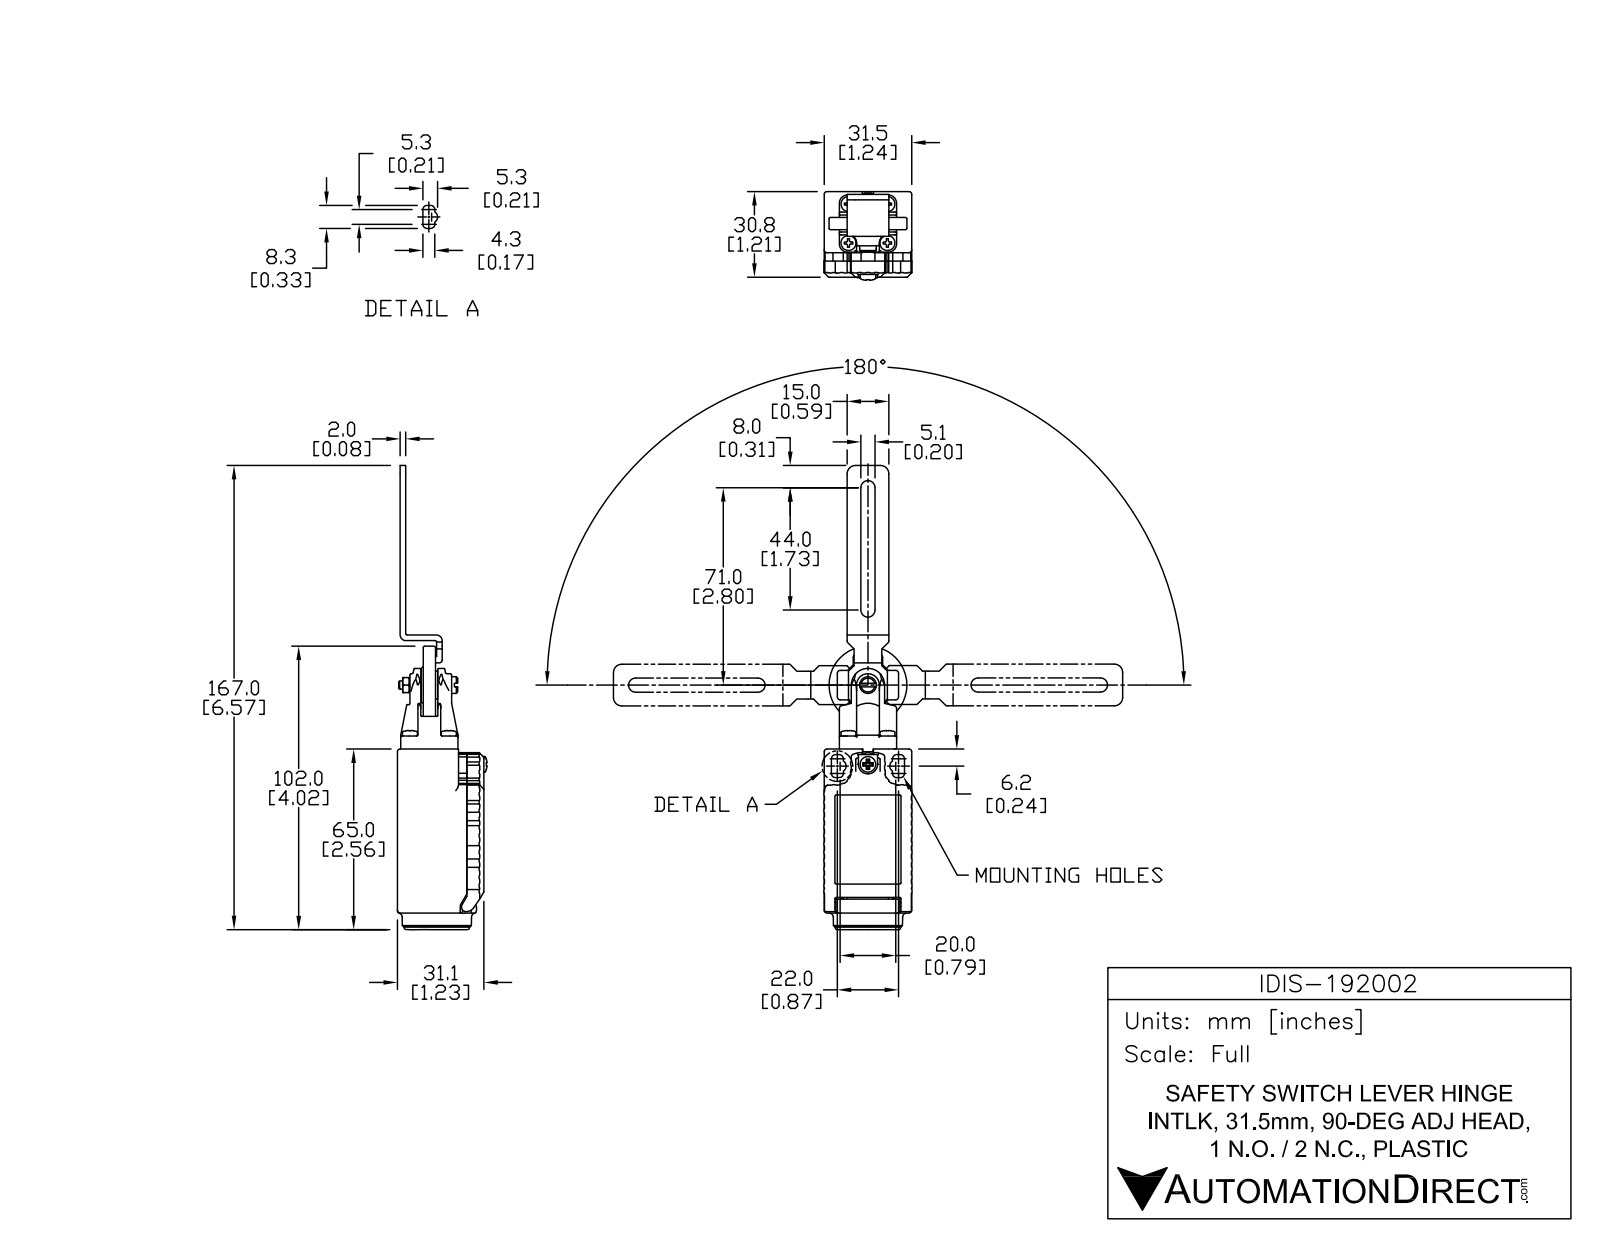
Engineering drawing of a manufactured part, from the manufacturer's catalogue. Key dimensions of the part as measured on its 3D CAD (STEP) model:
Part name (STEP PRODUCT): IDIS-192002
STEP written by: SolidWorks 2013 (AUTOMOTIVE_DESIGN)
Units: millimetres
Bodies: 1 solid, 668 faces (270 planar, 240 cylindrical, 158 other)
Overall size (bounding box): 176.7 × 32.2 × 31.5
Volume: 67 552 mm³ · Surface area: 21 014 mm²
Round holes (diameter × count): ⌀4 ×2, ⌀3 ×1, ⌀16.19 ×1, ⌀18.5 ×1, ⌀21.2 ×1
Round bosses / shafts (diameter × count): ⌀5.4 ×4, ⌀28 ×1, ⌀25 ×1, ⌀23 ×1, ⌀17.19 ×1, ⌀13.4 ×1, ⌀10 ×1, ⌀6 ×1
Partial cylindrical surfaces — rounded edges, fillets, slot ends (radius × count): R0.5 ×71, R0.25 ×32, R1 ×11, R0.12 ×9, R1.5 ×8, R2.4 ×6, R3 ×6, R2 ×4
Main face-to-face distances: 31.5, 5.6, 0.5, 9.3, 1.9, 3.2, 2.8, 30.2, 20.9, 19
Hole centre spacings: 22, 88.58, 88.59
